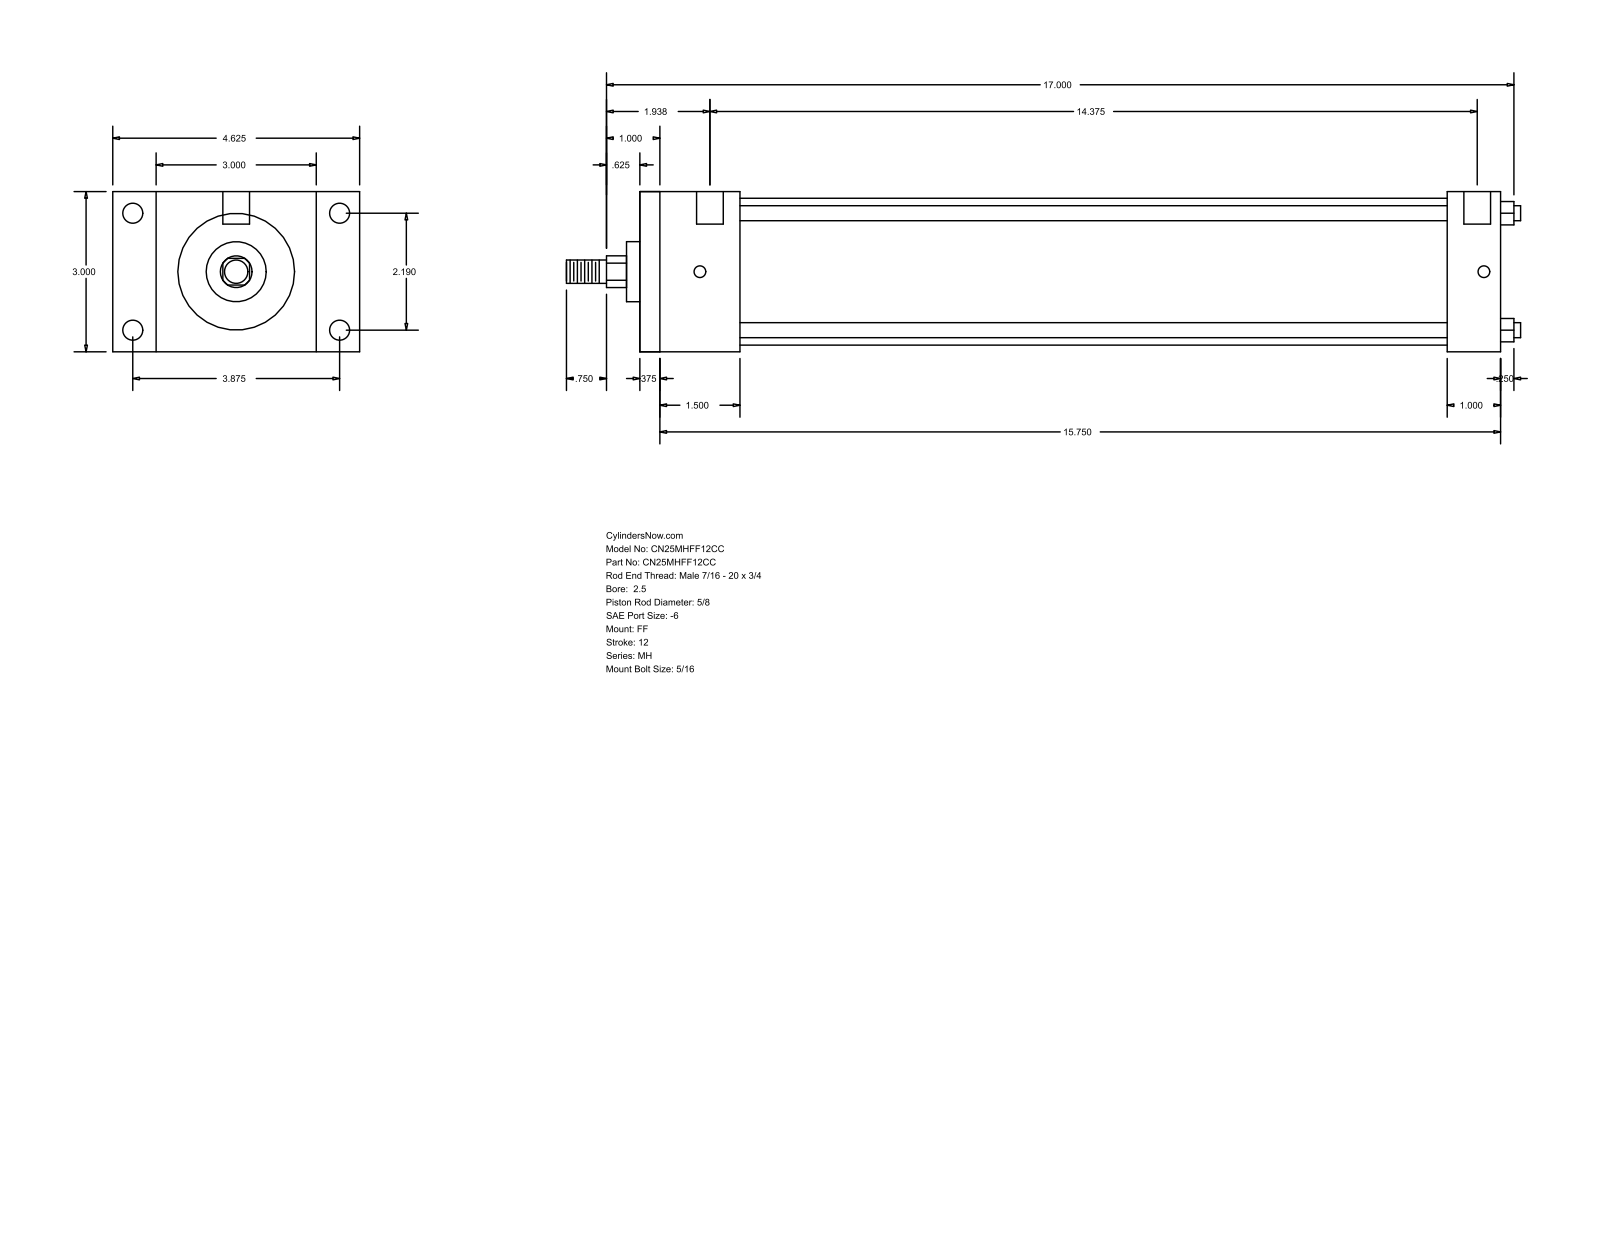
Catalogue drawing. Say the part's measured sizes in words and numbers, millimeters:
The part is named "MH_FF__0250_0.625". Its 3-D file was written by "GSSL Pune (CONFIG_CONTROL_DESIGN)". It is 0 solids with 92 faces: 64 planar, 28 cylindrical and 0 other. Overall it measures 454.02 by 117.47 by 76.2 millimeters. Round holes: 4 of diameter 5.56, 4 of diameter 9.53, 2 of diameter 12.7. Round bosses or shafts: 4 of diameter 7.14, 1 of diameter 69.85, 1 of diameter 28.57, 1 of diameter 15.88, 1 of diameter 11.11. Partial cylindrical surfaces (rounded edges, fillets, slot ends): 1 of radius 7.54. The main face-to-face distances are 76.2, 409.57, 400.05, 9.52, 25.4, 47.62, 384.17, 38.1, 374.65, 336.55. The hole center spacings are 55.62, 98.42, 113.05, 373.06, 3.17, 4.76, 365.13, 368.3.
